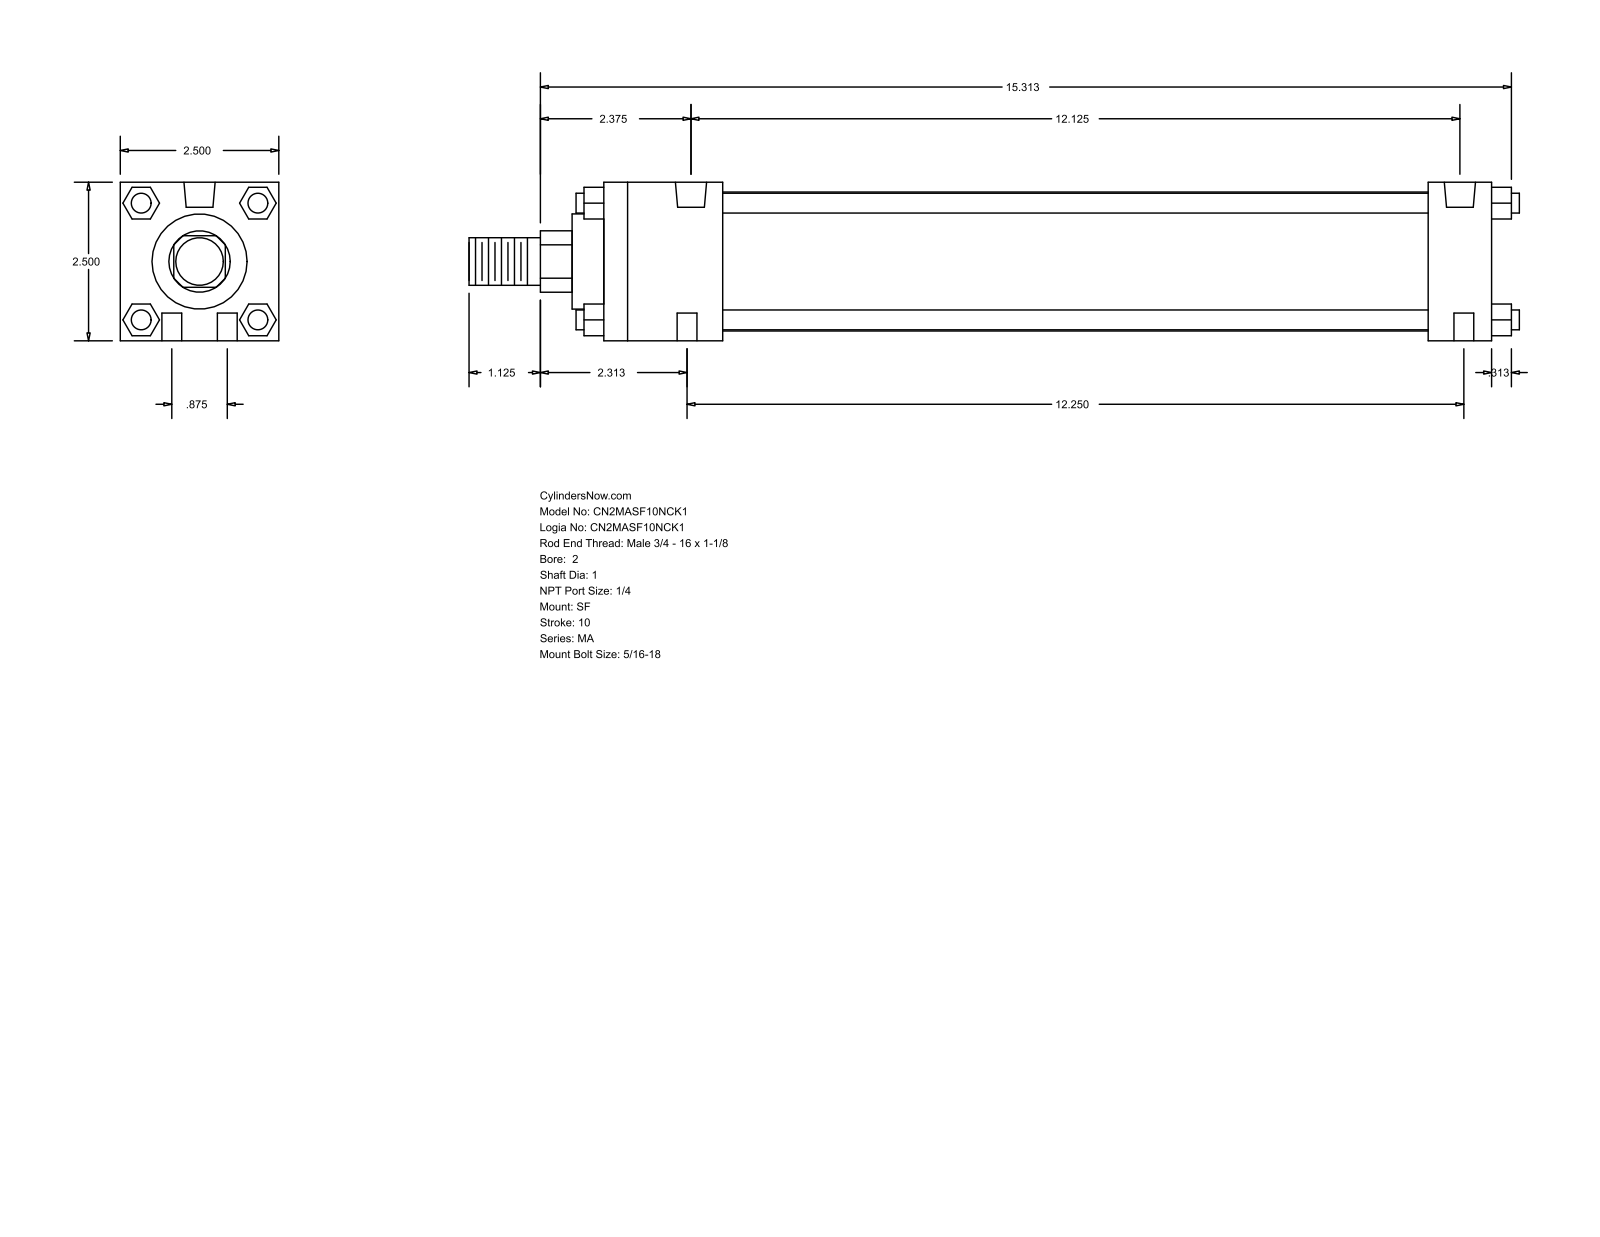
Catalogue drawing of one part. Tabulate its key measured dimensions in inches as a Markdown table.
| quantity | value |
| --- | --- |
| part name | MA_SF__0200_1 |
| STEP written by | GSSL Pune (CONFIG_CONTROL_DESIGN) |
| units | inches |
| bodies | 0 solids, 124 faces (94 planar, 30 cylindrical, 0 other) |
| overall size | 16.563 × 2.5 × 2.5 |
| round holes (diameter × count) | 0.313 × 6, 0.492 × 2 |
| round bosses / shafts (diameter × count) | 0.313 × 4, 2.19 × 1, 1.5 × 1, 1 × 1, 0.75 × 1 |
| partial cylindrical surfaces (radius × count) | 0.484 × 1 |
| main face-to-face distances | 2.5, 14, 0.5, 1, 13, 1.875, 11.125, 12.125, 0.92, 1.593 |
| hole center spacings | 0.442, 12.195, 0.875, 12.125, 12.25, 12.281 |
